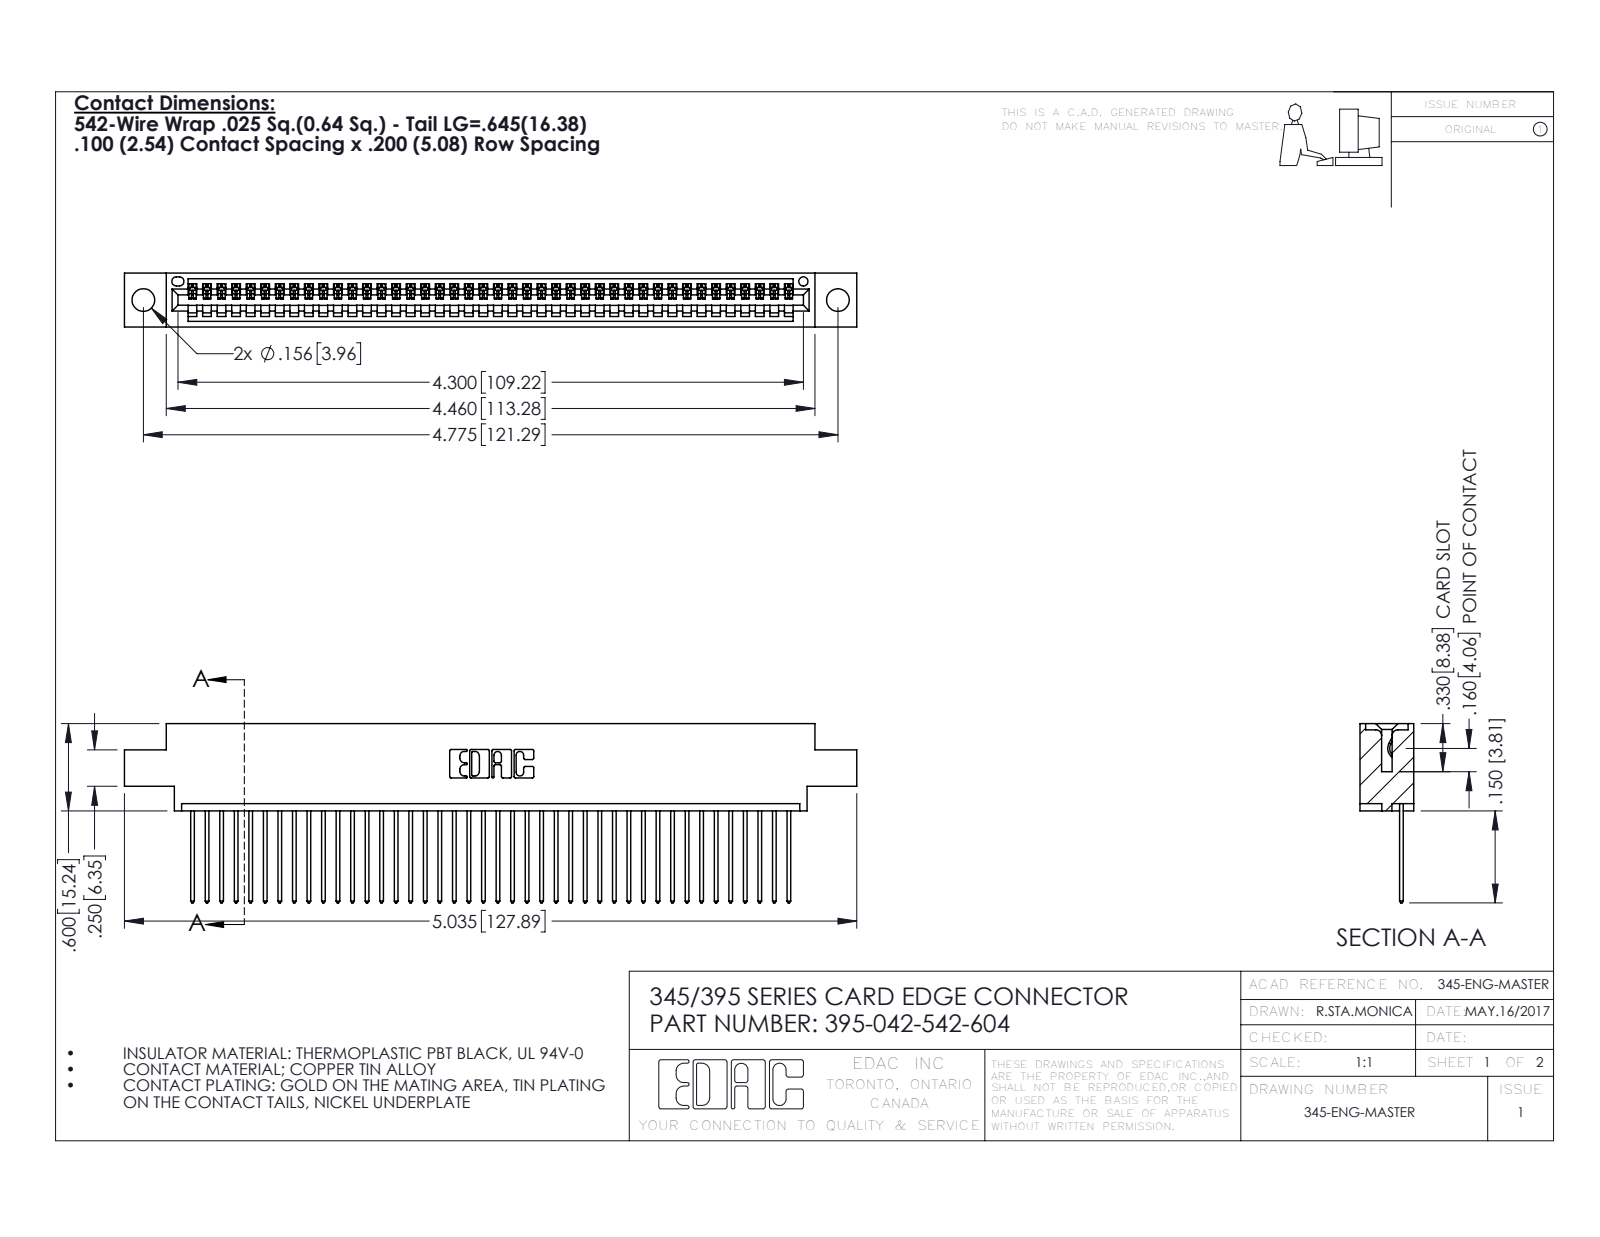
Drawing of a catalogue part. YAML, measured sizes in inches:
part_name: "345-292-001_345-293-142; 345 Part_0.170 Offset - 0.156 Dia-TH; 395-042-542-604"
step_written_by: "SolidWorks 2016 (CONFIG_CONTROL_DESIGN)"
units: inches
bodies: {solids: 43, faces: 2566, planar: 1764, cylindrical: 802, other: 0}
overall_size: [5.035, 1.232, 0.37]
volume: 0.735
surface_area: 25.61
round_holes:
  - {diameter: 0.156, count: 2}
  - {diameter: 0.064, count: 1}
partial_cylinders:
  - {radius: 0.006, count: 84}
  - {radius: 0.01, count: 84}
  - {radius: 0.01, count: 22}
  - {radius: 0.007, count: 6}
  - {radius: 0.031, count: 6}
  - {radius: 0.026, count: 3}
  - {radius: 0.031, count: 2}
  - {radius: 0.04, count: 2}
face_to_face_distances: [0.072, 0.298, 0.37, 0.098, 0.272, 0.025, 0.2, 0.225, 0.175, 0.149]
hole_center_spacings: [0.27, 4.539, 4.775]
